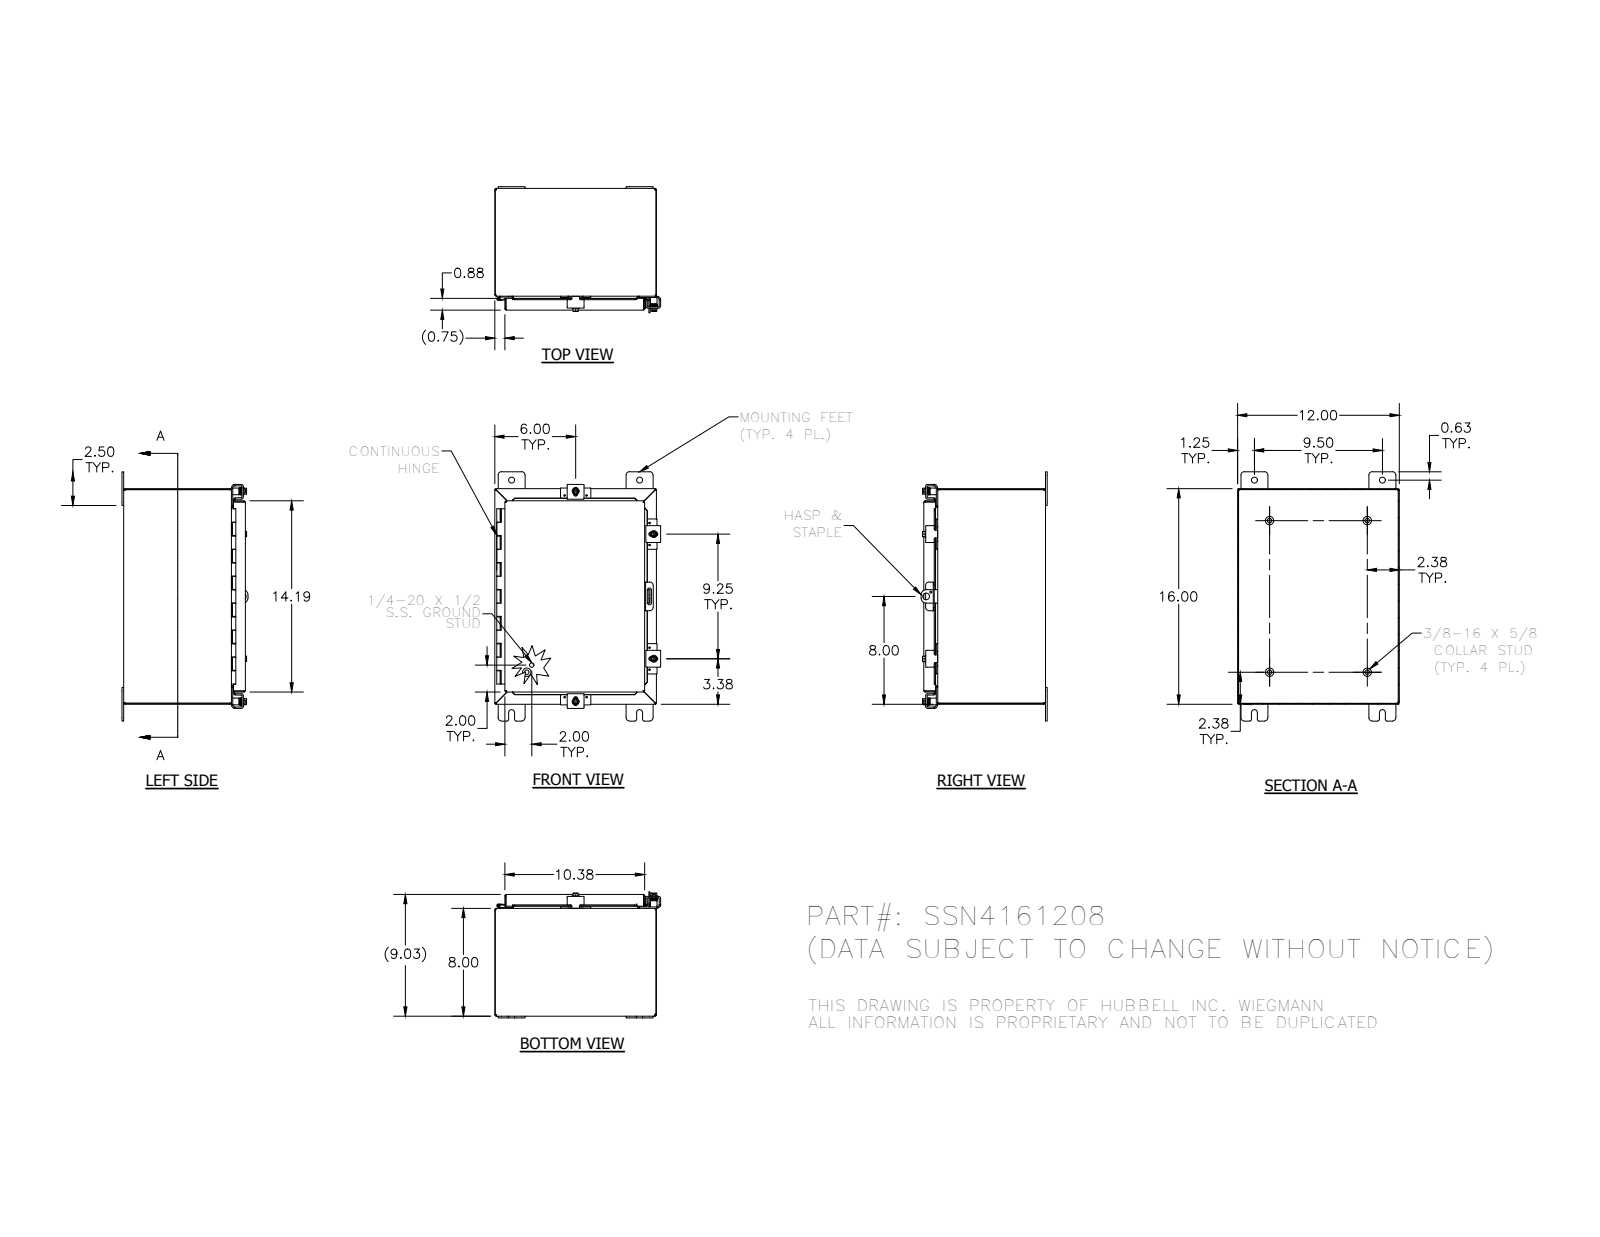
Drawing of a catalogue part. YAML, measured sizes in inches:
part_name: "HFW30825-3_1; 34871_1; HFW30825-4_1; 328136P_1 (+8 more)"
step_written_by: "SolidWorks 2014 (AUTOMOTIVE_DESIGN)"
units: inches
bodies: {solids: 37, faces: 1390, planar: 545, cylindrical: 604, other: 241}
overall_size: [18.5, 12.311, 9.355]
volume: 81.22
surface_area: 2113
round_holes:
  - {diameter: 0.11, count: 8}
  - {diameter: 0.211, count: 4}
  - {diameter: 0.281, count: 4}
  - {diameter: 0.3, count: 4}
  - {diameter: 0.438, count: 4}
  - {diameter: 0.125, count: 1}
  - {diameter: 0.156, count: 1}
  - {diameter: 0.5, count: 1}
round_bosses_or_shafts:
  - {diameter: 0.33, count: 6}
  - {diameter: 0.25, count: 6}
  - {diameter: 0.625, count: 4}
  - {diameter: 0.52, count: 4}
  - {diameter: 0.5, count: 4}
  - {diameter: 0.35, count: 4}
  - {diameter: 0.337, count: 1}
  - {diameter: 0.12, count: 1}
partial_cylinders:
  - {radius: 0.03, count: 49}
  - {radius: 0.125, count: 33}
  - {radius: 0.25, count: 29}
  - {radius: 0.031, count: 23}
  - {radius: 0.105, count: 23}
  - {radius: 0.062, count: 11}
  - {radius: 0.07, count: 8}
  - {radius: 0.141, count: 8}
face_to_face_distances: [0.074, 8.959, 11.926, 15.926, 8.885, 9.033, 7.926, 1.033, 12, 11.852]
hole_center_spacings: [0.876, 15.311, 9.25, 0.876, 1.625, 1.625, 3.939, 4.1]
